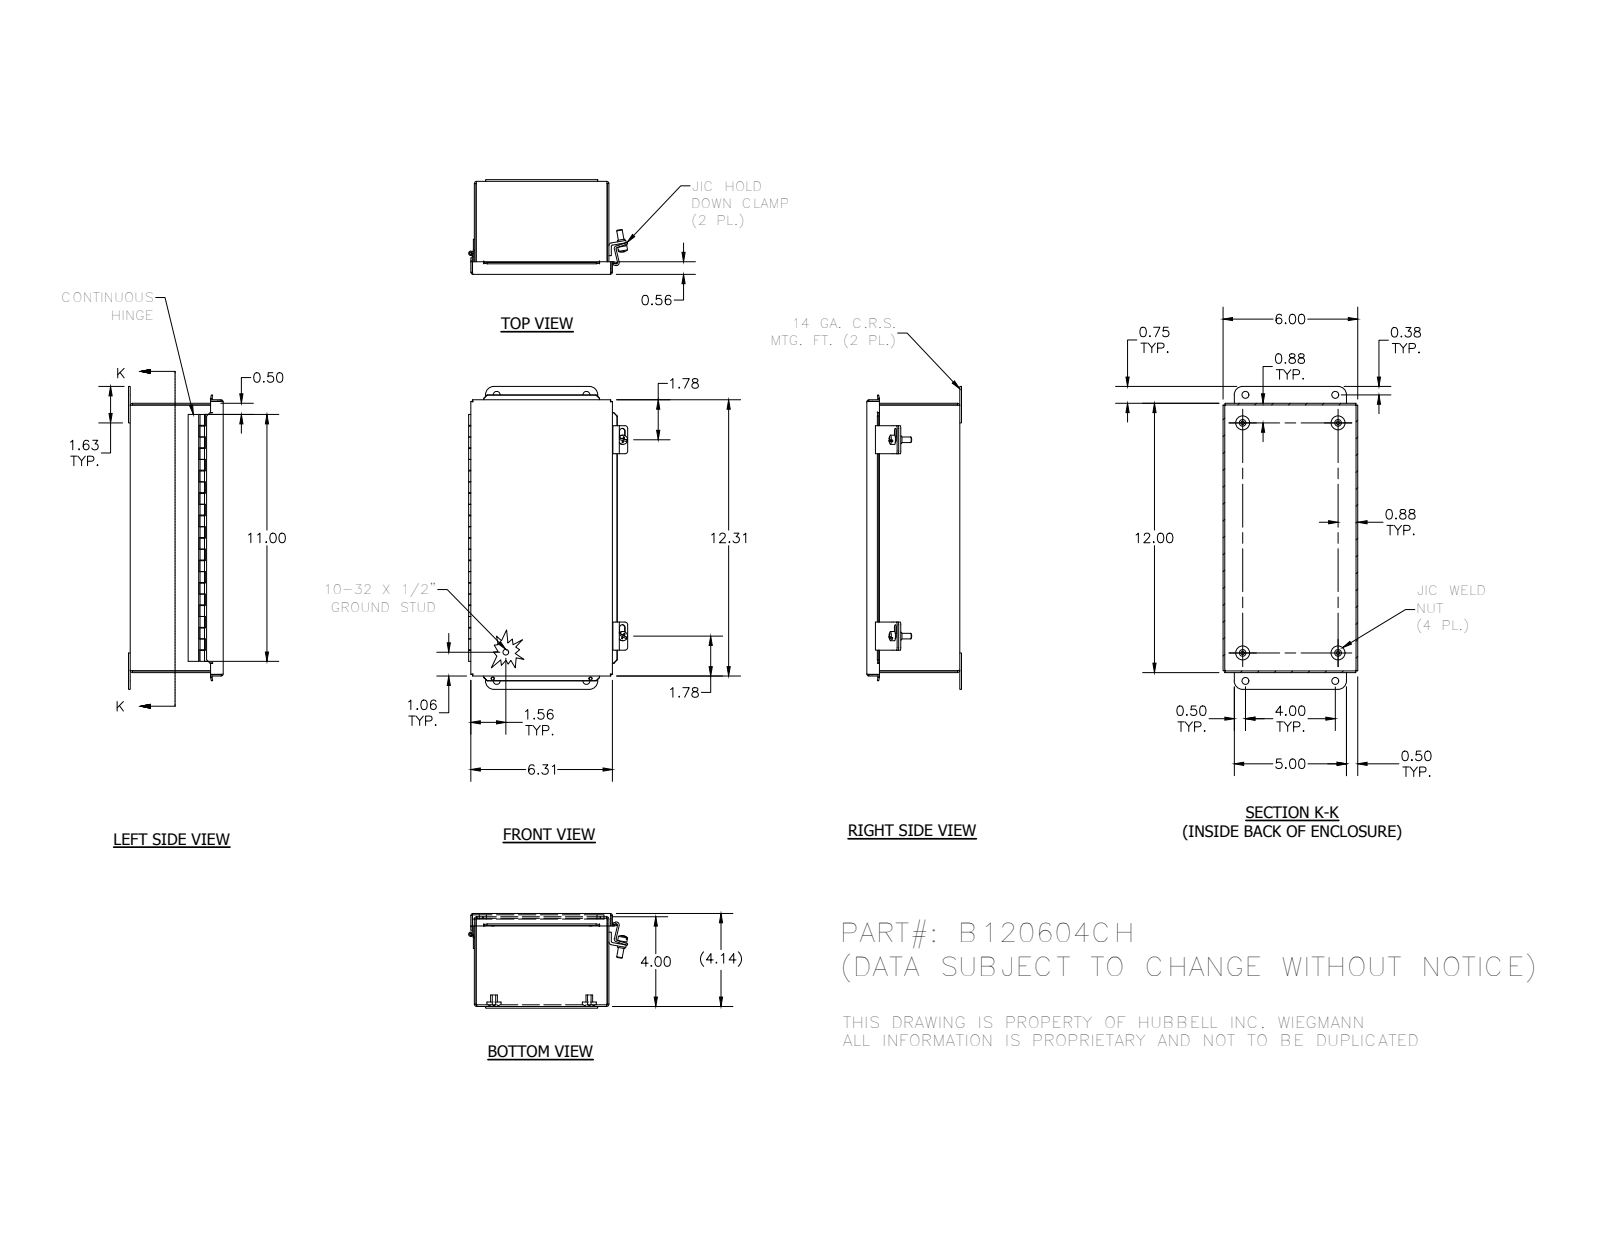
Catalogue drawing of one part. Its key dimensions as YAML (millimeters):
part_name: "B120604CH; 3499; 3482; C1001 (+8 more)"
step_written_by: "Autodesk Inventor 2012 (AUTOMOTIVE_DESIGN)"
units: millimeters
bodies: {solids: 20, faces: 499, planar: 323, cylindrical: 131, other: 45}
overall_size: [342.9, 180, 107.2]
volume: 483600
surface_area: 520200
round_holes:
  - {diameter: 4, count: 4}
  - {diameter: 7.9, count: 4}
  - {diameter: 3.6, count: 2}
  - {diameter: 5, count: 2}
  - {diameter: 2.9, count: 1}
round_bosses_or_shafts:
  - {diameter: 15.9, count: 4}
  - {diameter: 7.6, count: 4}
  - {diameter: 6.4, count: 3}
  - {diameter: 10.4, count: 2}
  - {diameter: 8.7, count: 2}
  - {diameter: 5.1, count: 1}
  - {diameter: 4.8, count: 1}
  - {diameter: 2.5, count: 1}
partial_cylinders:
  - {radius: 0.8, count: 15}
  - {radius: 2.7, count: 8}
  - {radius: 3.2, count: 8}
  - {radius: 2.4, count: 7}
  - {radius: 3.4, count: 4}
  - {radius: 9.5, count: 4}
  - {radius: 1.6, count: 3}
  - {radius: 3.2, count: 3}
face_to_face_distances: [1.9, 150.5, 103.7, 1.6, 105.3, 101.8, 103.4, 152.4, 148.6, 302.9]
hole_center_spacings: [31.9, 109.5, 292.1, 310.3, 101.6, 108, 323.9, 339.4]
